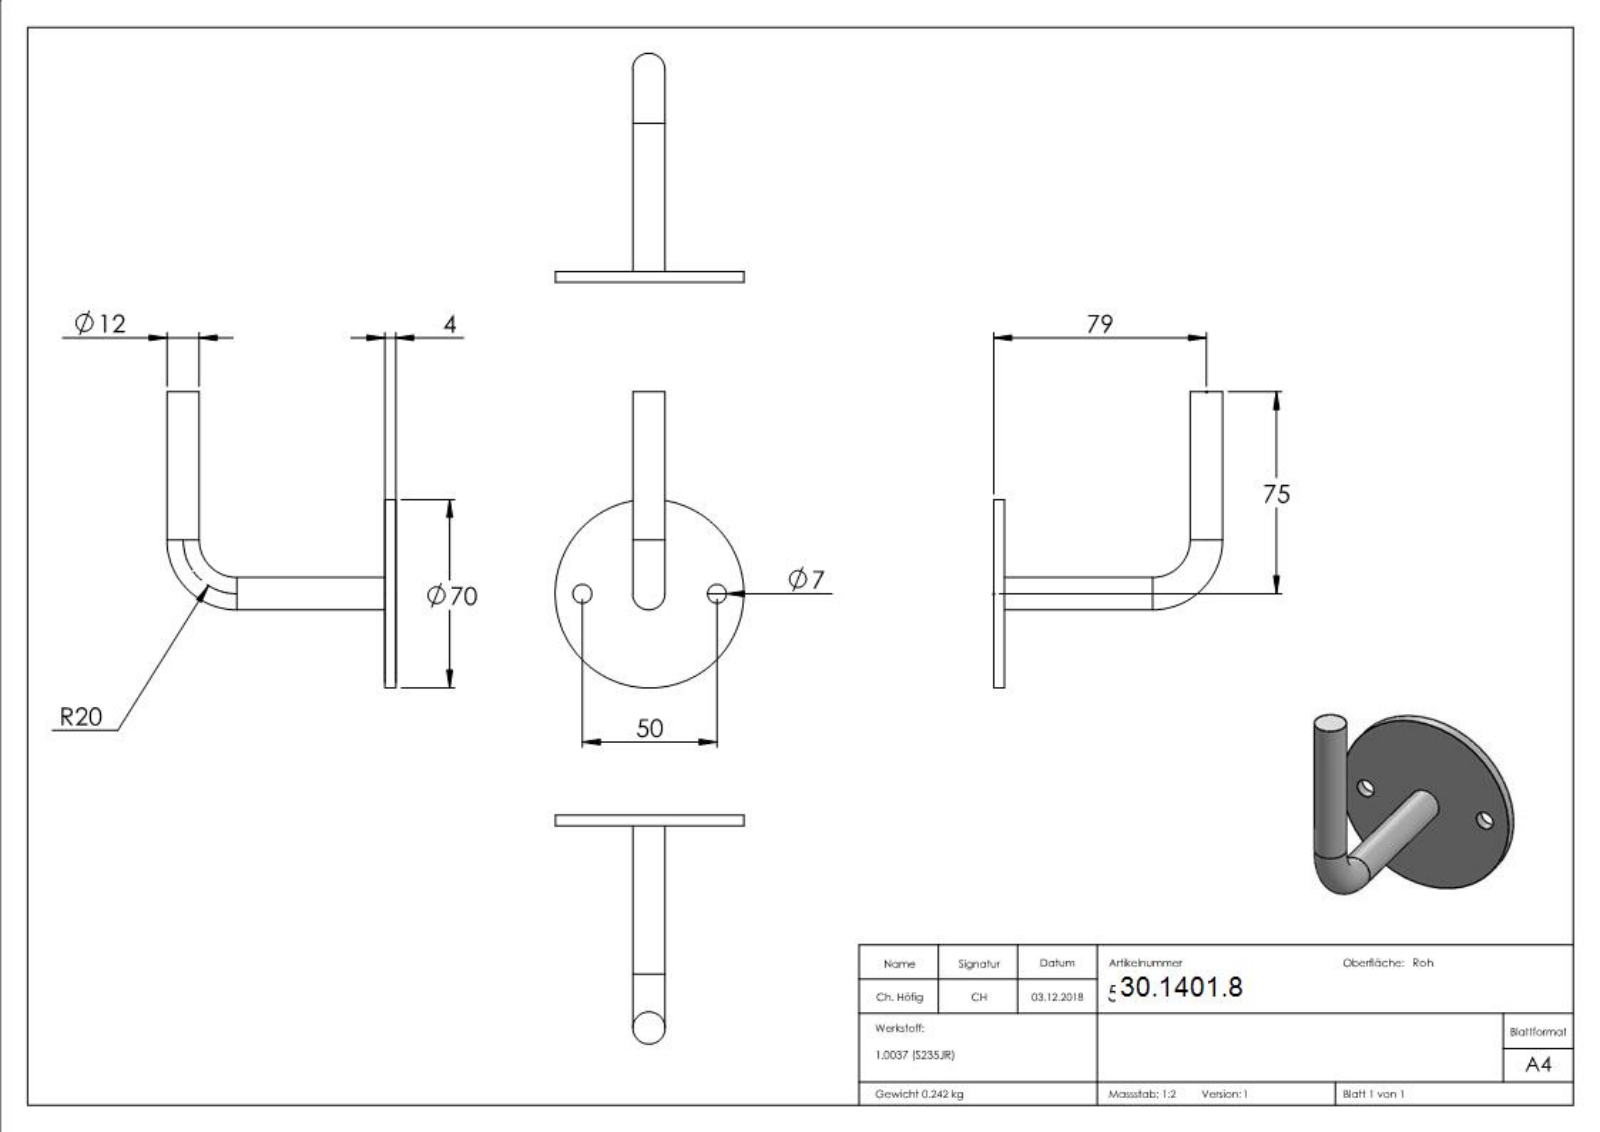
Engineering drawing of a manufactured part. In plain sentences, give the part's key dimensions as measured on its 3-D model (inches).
The part is named "50300-ST". Its 3-D file was written by "SolidWorks 2015 (CONFIG_CONTROL_DESIGN)". It is 1 solid with 15 faces: 3 planar, 10 cylindrical and 2 other. Overall it measures 4.331 by 3.346 by 2.756 inches. Its volume is 1.897 cubic inches and its surface area 21.59 square inches. Round holes: 2 of diameter 0.276. Round bosses or shafts: 2 of diameter 0.472, 1 of diameter 2.756. The main face-to-face distances are 0.157. The hole center spacings are 1.969.
